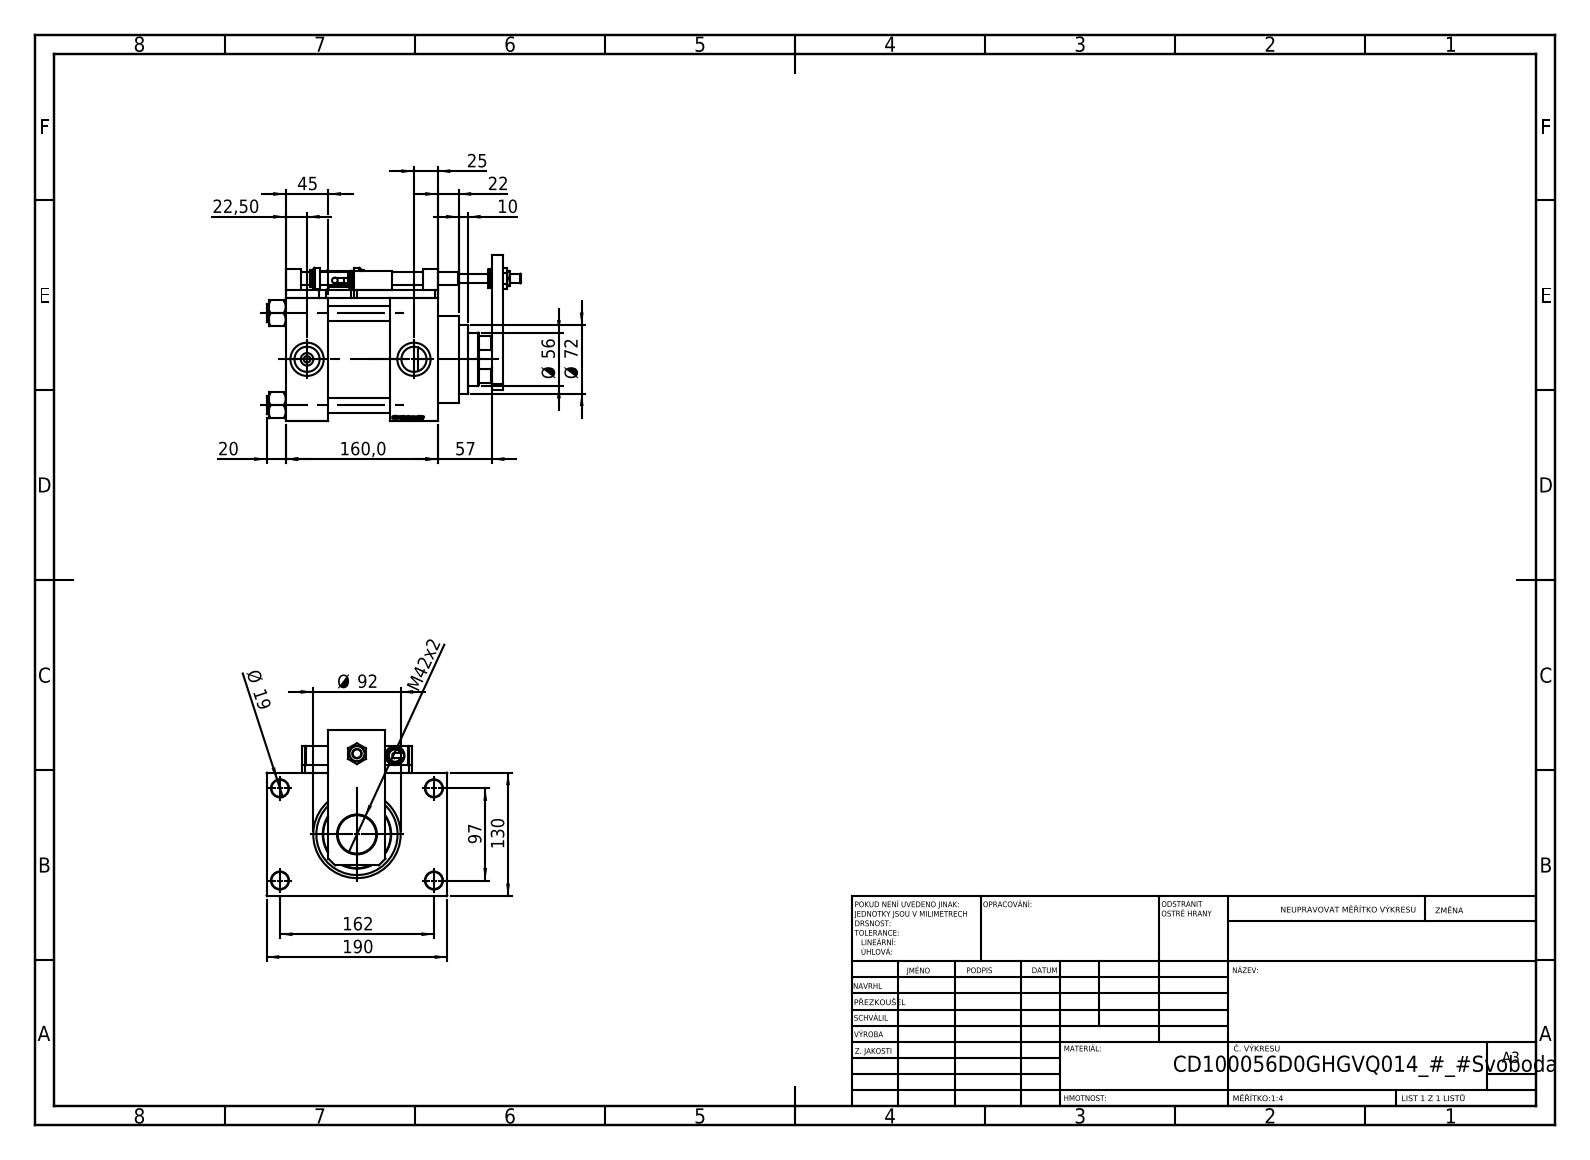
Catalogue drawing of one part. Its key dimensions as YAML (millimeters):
part_name: "V215CD_VCP_D; V215CD_SWITCH_Q_ZARAZKA; V215CD_SWITCH_Q_MAGNET; V215CD_SWITCH_Q_DIMA (+8 more)"
step_written_by: "SolidWorks 2019 (CONFIG_CONTROL_DESIGN)"
units: millimeters
bodies: {solids: 24, faces: 1379, planar: 666, cylindrical: 156, other: 557}
overall_size: [267.5, 190, 175]
volume: 2924000
surface_area: 452449
round_holes:
  - {diameter: 8.5, count: 4}
  - {diameter: 13.5, count: 4}
  - {diameter: 16, count: 4}
  - {diameter: 18, count: 4}
  - {diameter: 7, count: 2}
  - {diameter: 26.44, count: 2}
  - {diameter: 35, count: 2}
  - {diameter: 10, count: 1}
  - {diameter: 14, count: 1}
  - {diameter: 40.5, count: 1}
  - {diameter: 42, count: 1}
  - {diameter: 56, count: 1}
round_bosses_or_shafts:
  - {diameter: 19, count: 4}
  - {diameter: 20, count: 3}
  - {diameter: 16, count: 2}
  - {diameter: 14, count: 2}
  - {diameter: 6, count: 2}
  - {diameter: 106, count: 1}
  - {diameter: 92, count: 1}
  - {diameter: 72, count: 1}
partial_cylinders:
  - {radius: 7.5, count: 4}
  - {radius: 27, count: 1}
face_to_face_distances: [160, 130, 65, 115, 45, 8, 110, 50, 138, 30]
hole_center_spacings: [32.55, 68.52, 94.41, 96.9, 102.27, 129.45, 161.73, 32]
